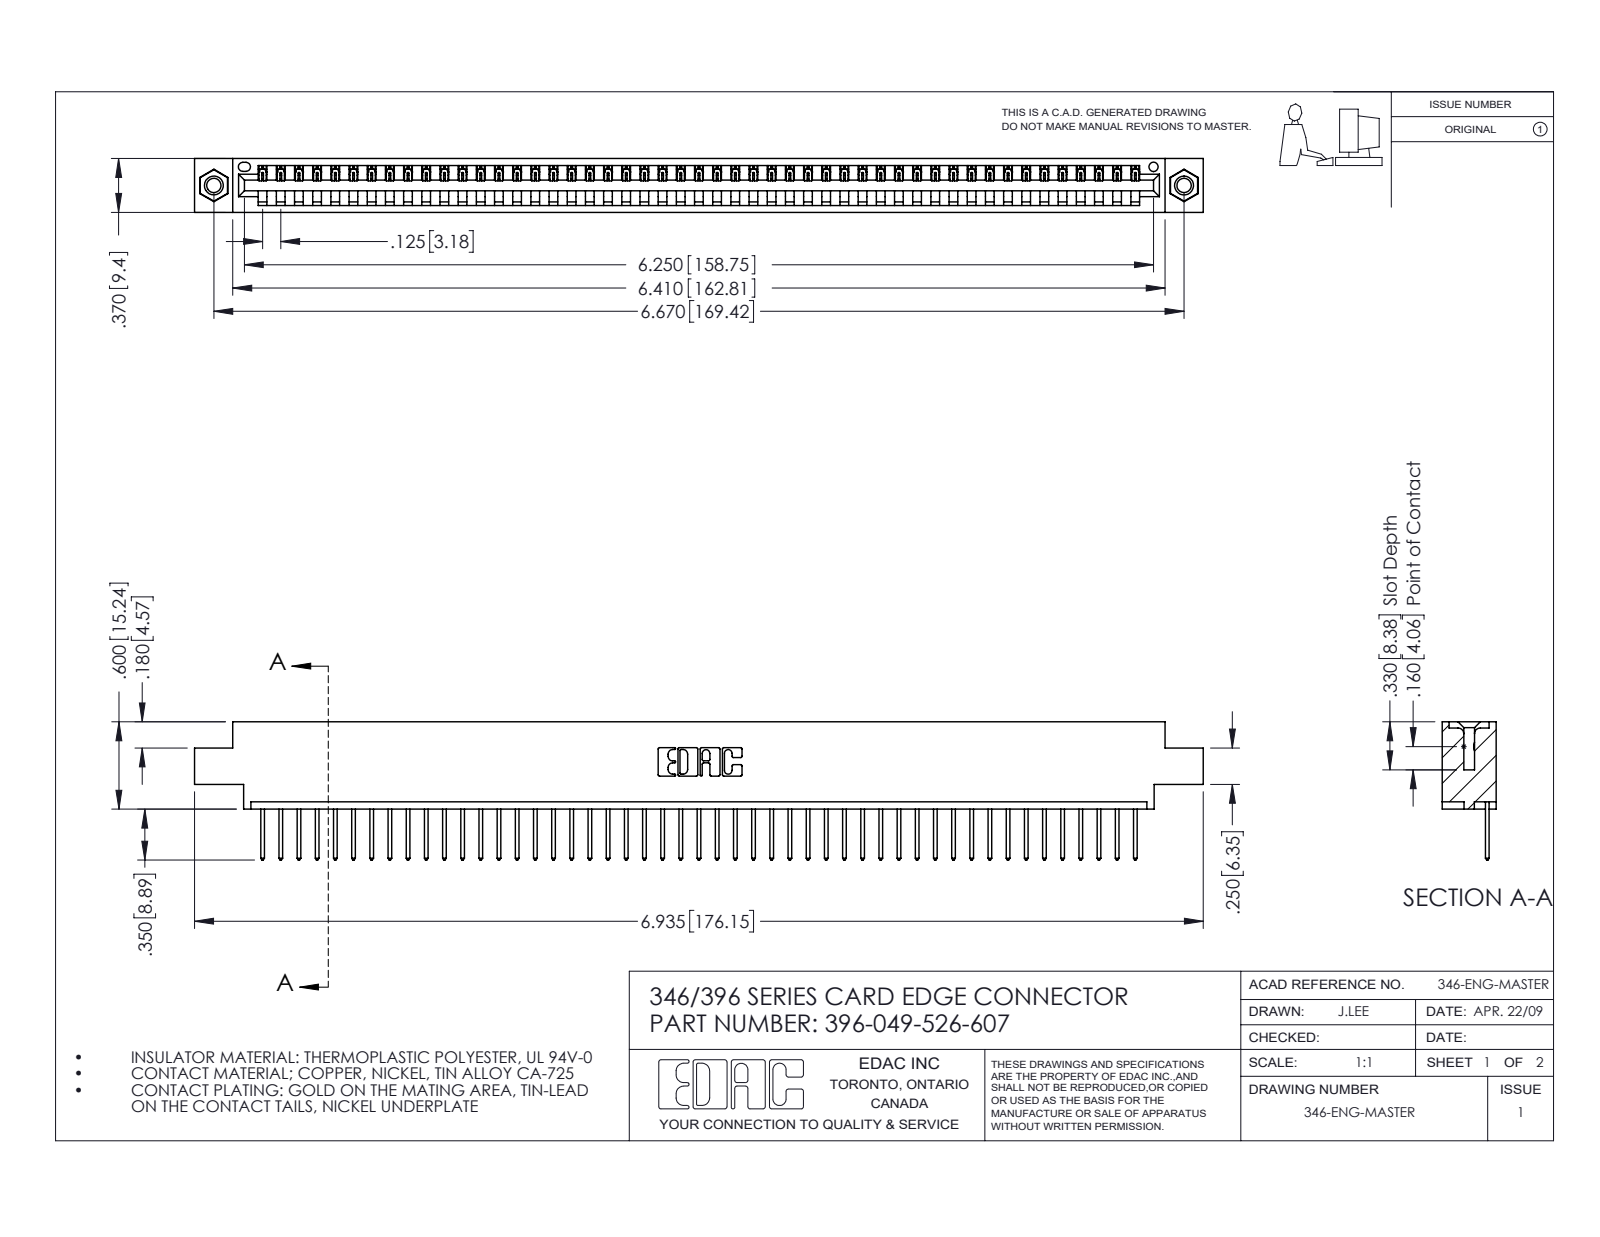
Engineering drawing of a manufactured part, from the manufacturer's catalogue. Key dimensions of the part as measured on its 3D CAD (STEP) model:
Part name (STEP PRODUCT): 396-049-526-607; 345-250-001_345-250-005-103; 345-292-001_345-293-126; 346 Part_0.170 Offset - 0.156 Dia-TI
STEP written by: SolidWorks 2016 (CONFIG_CONTROL_DESIGN)
Units: inches
Bodies: 52 solids, 3028 faces (2072 planar, 940 cylindrical, 16 other)
Overall size (bounding box): 6.935 × 0.95 × 0.37
Volume: 1.019 in³ · Surface area: 32.7 in²
Round holes (diameter × count): ⌀0.098 ×2, ⌀0.125 ×2, ⌀0.156 ×2, ⌀0.064 ×1
Round bosses / shafts (diameter × count): ⌀0.155 ×2
Partial cylindrical surfaces — rounded edges, fillets, slot ends (radius × count): R0.006 ×98, R0.01 ×98, R0.01 ×22, R0.007 ×6, R0.031 ×6, R0.026 ×3, R0.031 ×2, R0.04 ×2
Main face-to-face distances: 0.048, 0.322, 0.37, 0.25, 0.072, 0.298, 0.025, 0.222, 0.148, 0.1
Hole centre spacings: 0.246, 6.461, 6.67
